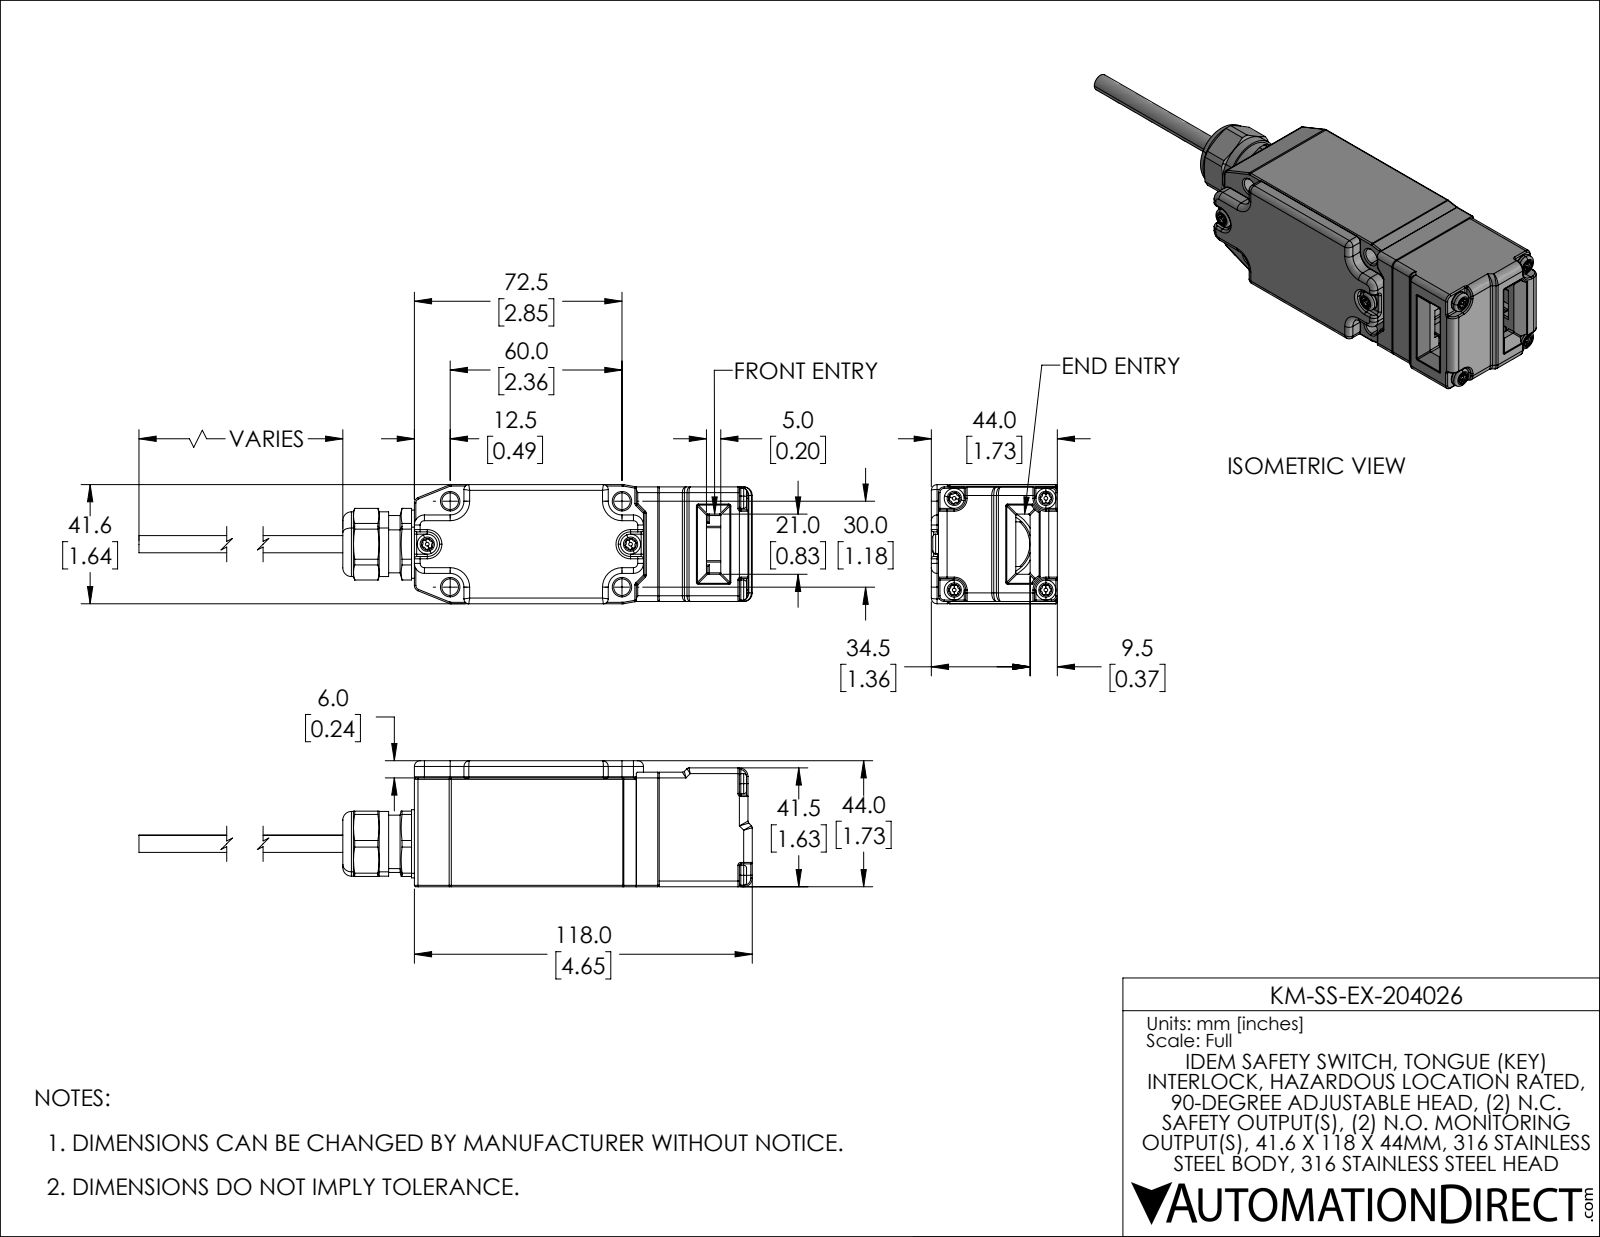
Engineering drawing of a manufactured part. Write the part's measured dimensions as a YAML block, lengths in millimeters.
part_name: "KM-SS-EX-204026"
step_written_by: "SolidWorks 2021 (AUTOMOTIVE_DESIGN)"
units: millimeters
bodies: {solids: 19, faces: 2310, planar: 659, cylindrical: 859, other: 792}
overall_size: [202, 44, 41.6]
volume: 90960
surface_area: 64970
round_holes:
  - {diameter: 3.8, count: 6}
  - {diameter: 4, count: 6}
  - {diameter: 3, count: 5}
  - {diameter: 4.2, count: 4}
  - {diameter: 5.8, count: 4}
  - {diameter: 2.2, count: 2}
  - {diameter: 4.3, count: 2}
  - {diameter: 5, count: 2}
  - {diameter: 2, count: 1}
  - {diameter: 3.1, count: 1}
  - {diameter: 3.1, count: 1}
  - {diameter: 3.5, count: 1}
round_bosses_or_shafts:
  - {diameter: 6, count: 9}
  - {diameter: 7, count: 6}
  - {diameter: 1.3, count: 6}
  - {diameter: 3.5, count: 4}
  - {diameter: 4.8, count: 2}
  - {diameter: 23.8, count: 1}
  - {diameter: 22.6, count: 1}
  - {diameter: 20, count: 1}
partial_cylinders:
  - {radius: 0.5, count: 301}
  - {radius: 1, count: 59}
  - {radius: 0.4, count: 24}
  - {radius: 2, count: 22}
  - {radius: 0.1, count: 16}
  - {radius: 0.3, count: 16}
  - {radius: 0.2, count: 14}
  - {radius: 0.8, count: 10}
face_to_face_distances: [2.2, 3, 38.6, 0.8, 40.8, 37.8, 41.6, 2.5, 44, 40]
hole_center_spacings: [22.6, 32, 7.3, 9, 10.2, 10.5, 12.8, 15.3]
